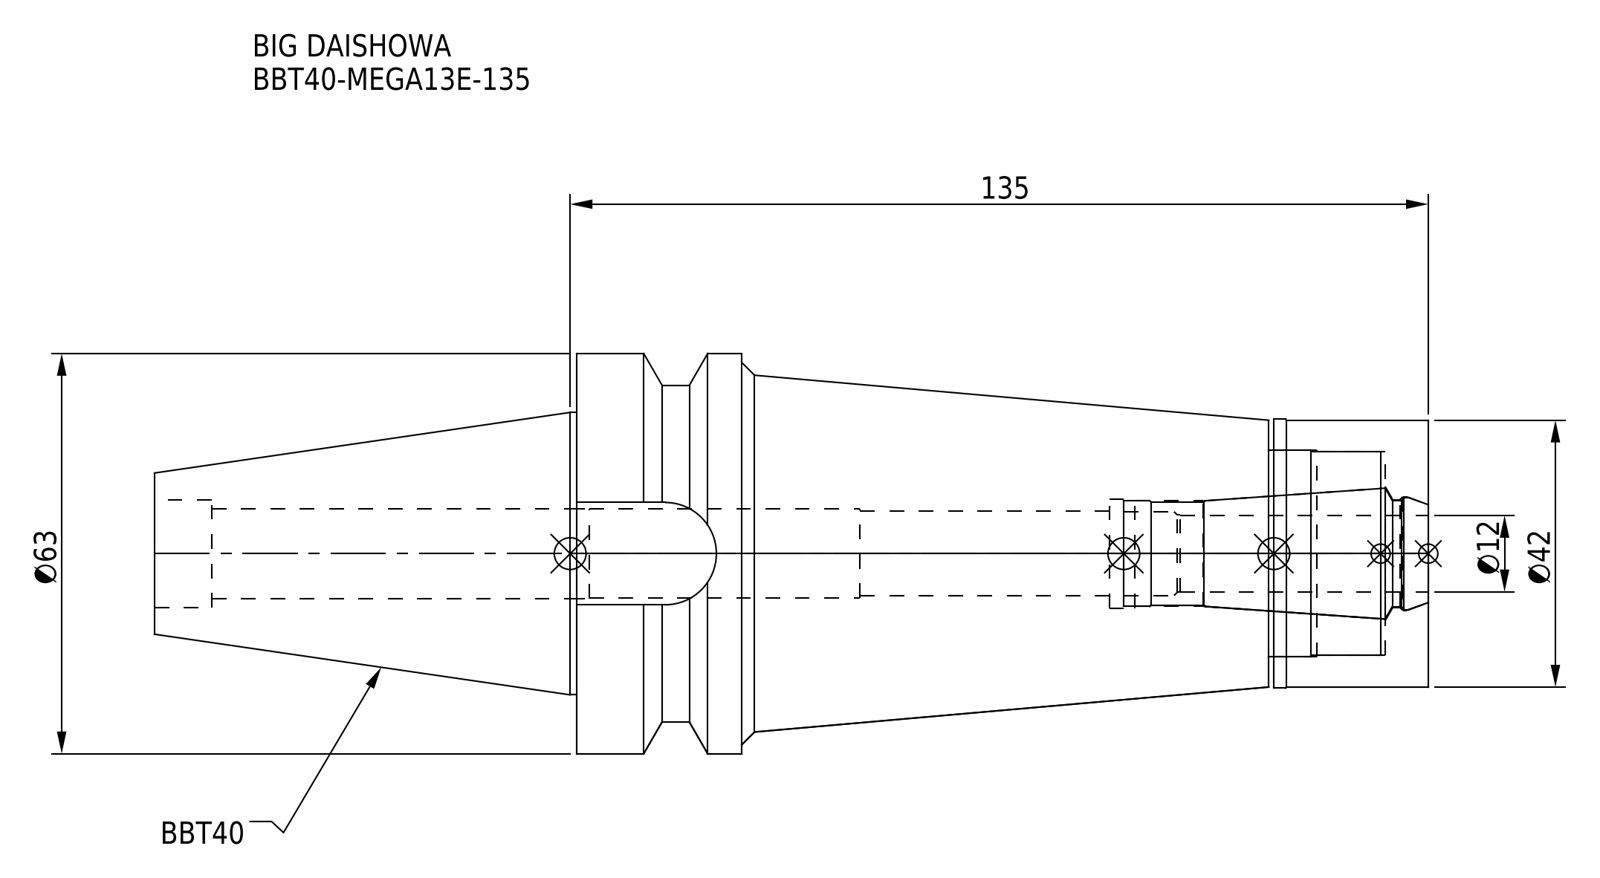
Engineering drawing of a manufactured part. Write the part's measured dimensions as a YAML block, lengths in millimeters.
part_name: "MEN13_1.stp; BBT40-MEGA13E-135-120.stp; BBT40-MEGA13E-135-120-FreeParts; DXF_TEMP_ASSY_ASM_4_ASM.stp (+3 more)"
step_written_by: "SolidWorks 2019 (CONFIG_CONTROL_DESIGN)"
units: millimeters
bodies: {solids: 2, faces: 81, planar: 21, cylindrical: 40, other: 20}
overall_size: [200.4, 63, 63]
volume: 292884
surface_area: 48567
round_holes:
  - {diameter: 13.3, count: 1}
  - {diameter: 14, count: 1}
  - {diameter: 14.2, count: 1}
  - {diameter: 16.6, count: 1}
  - {diameter: 17, count: 1}
  - {diameter: 17.2, count: 1}
  - {diameter: 17.9, count: 1}
  - {diameter: 32, count: 1}
  - {diameter: 32.5, count: 1}
round_bosses_or_shafts:
  - {diameter: 63, count: 1}
  - {diameter: 53, count: 1}
  - {diameter: 44.45, count: 1}
  - {diameter: 42.3, count: 1}
  - {diameter: 42, count: 1}
partial_cylinders:
  - {radius: 8.05, count: 1}
face_to_face_distances: [134, 25.1, 24.3, 109.7, 0.8, 108.9, 6.8, 17.5, 7.5, 16.8]
